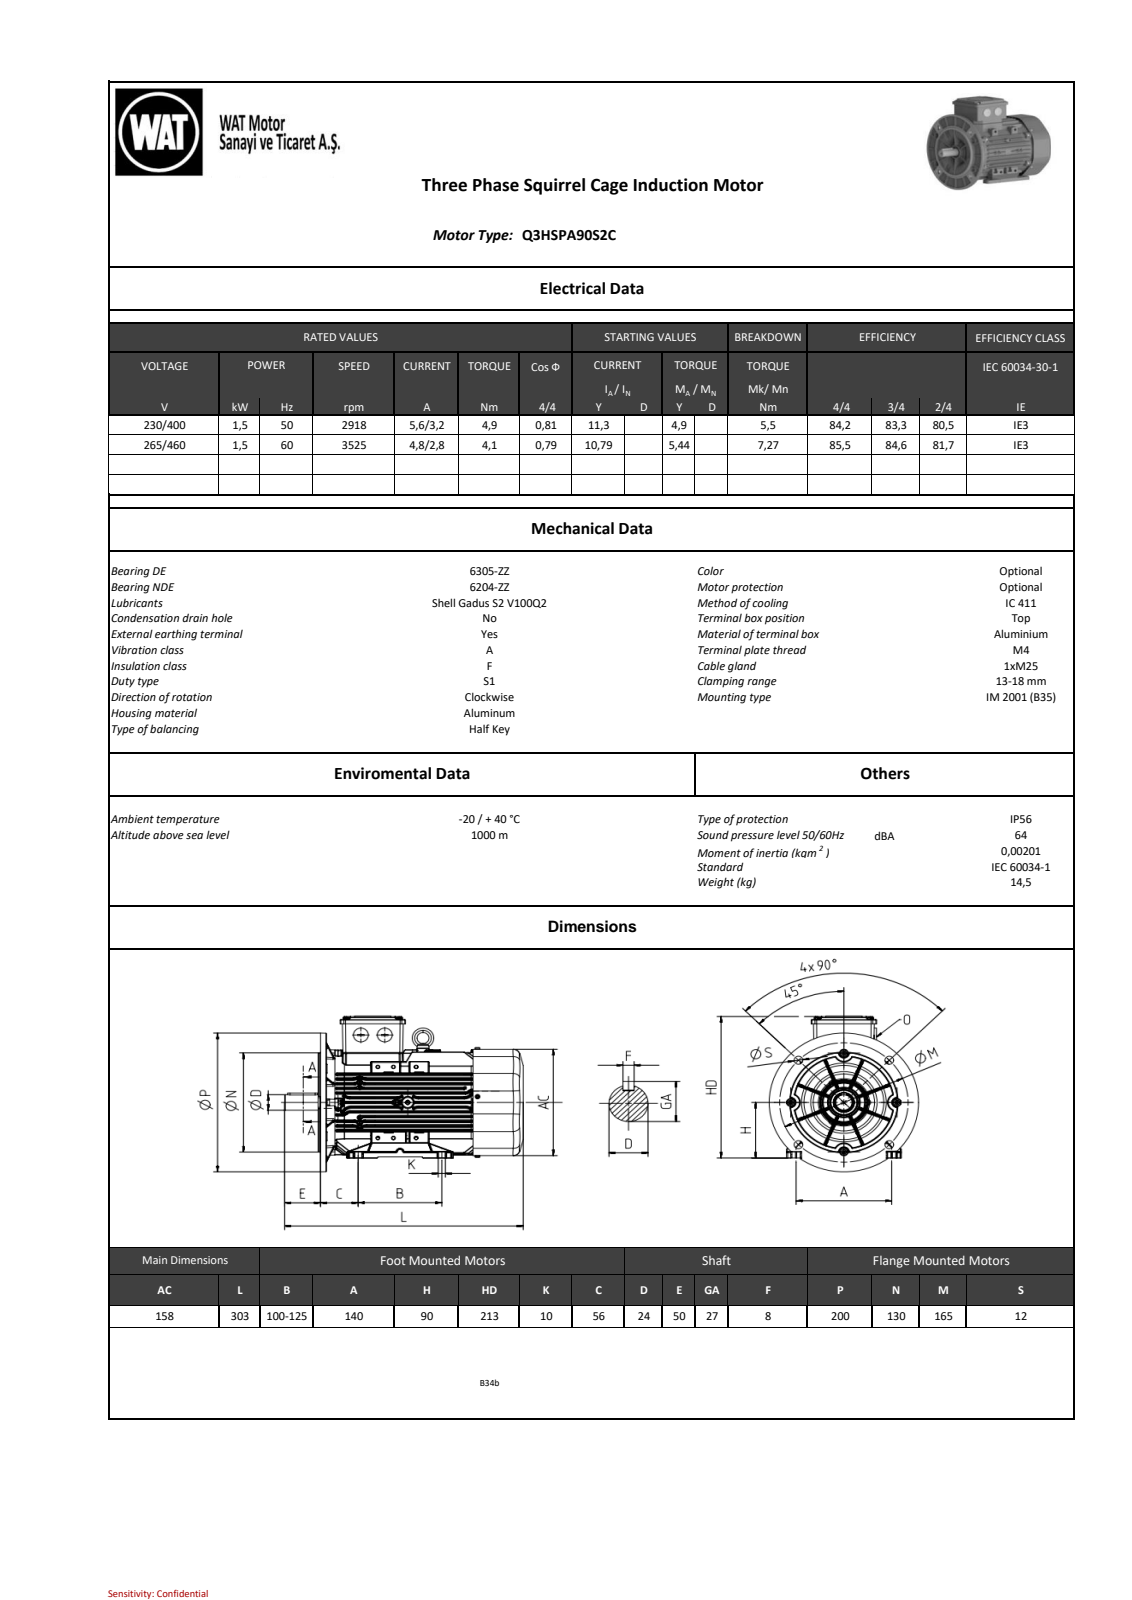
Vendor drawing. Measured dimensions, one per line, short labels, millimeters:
name: Ar311A3C0609zm5f
written by: SIEMENS PLM Software NX 9.0 (AUTOMOTIVE_DESIGN)
unit: mm
bodies: 0 solids, 8001 faces (1636 planar, 2624 cylindrical, 3741 other)
size: 303 × 221.5 × 200
holes: 4× ⌀3.5, 4× ⌀12, 3× ⌀3, 2× ⌀3.99, 2× ⌀4.6, 1× ⌀4.13, 1× ⌀5.5, 1× ⌀6.8, 1× ⌀8, 1× ⌀8.4, 1× ⌀40, 1× ⌀57.4
bosses: 4× ⌀6, 3× ⌀8.33, 2× ⌀11.6, 2× ⌀10, 1× ⌀146.5, 1× ⌀130, 1× ⌀68.9, 1× ⌀61
rounds: 1025× R0.5, 319× R0.8, 240× R1, 32× R1.5, 21× R2, 16× R2.5, 14× R0.4, 14× R4
face distances: 6, 1, 4, 11, 138, 158, 35.5, 36.5, 169, 5
hole spacings: 25.5, 82.51, 116.68, 6.76, 20, 44.17, 58.25, 66.95
